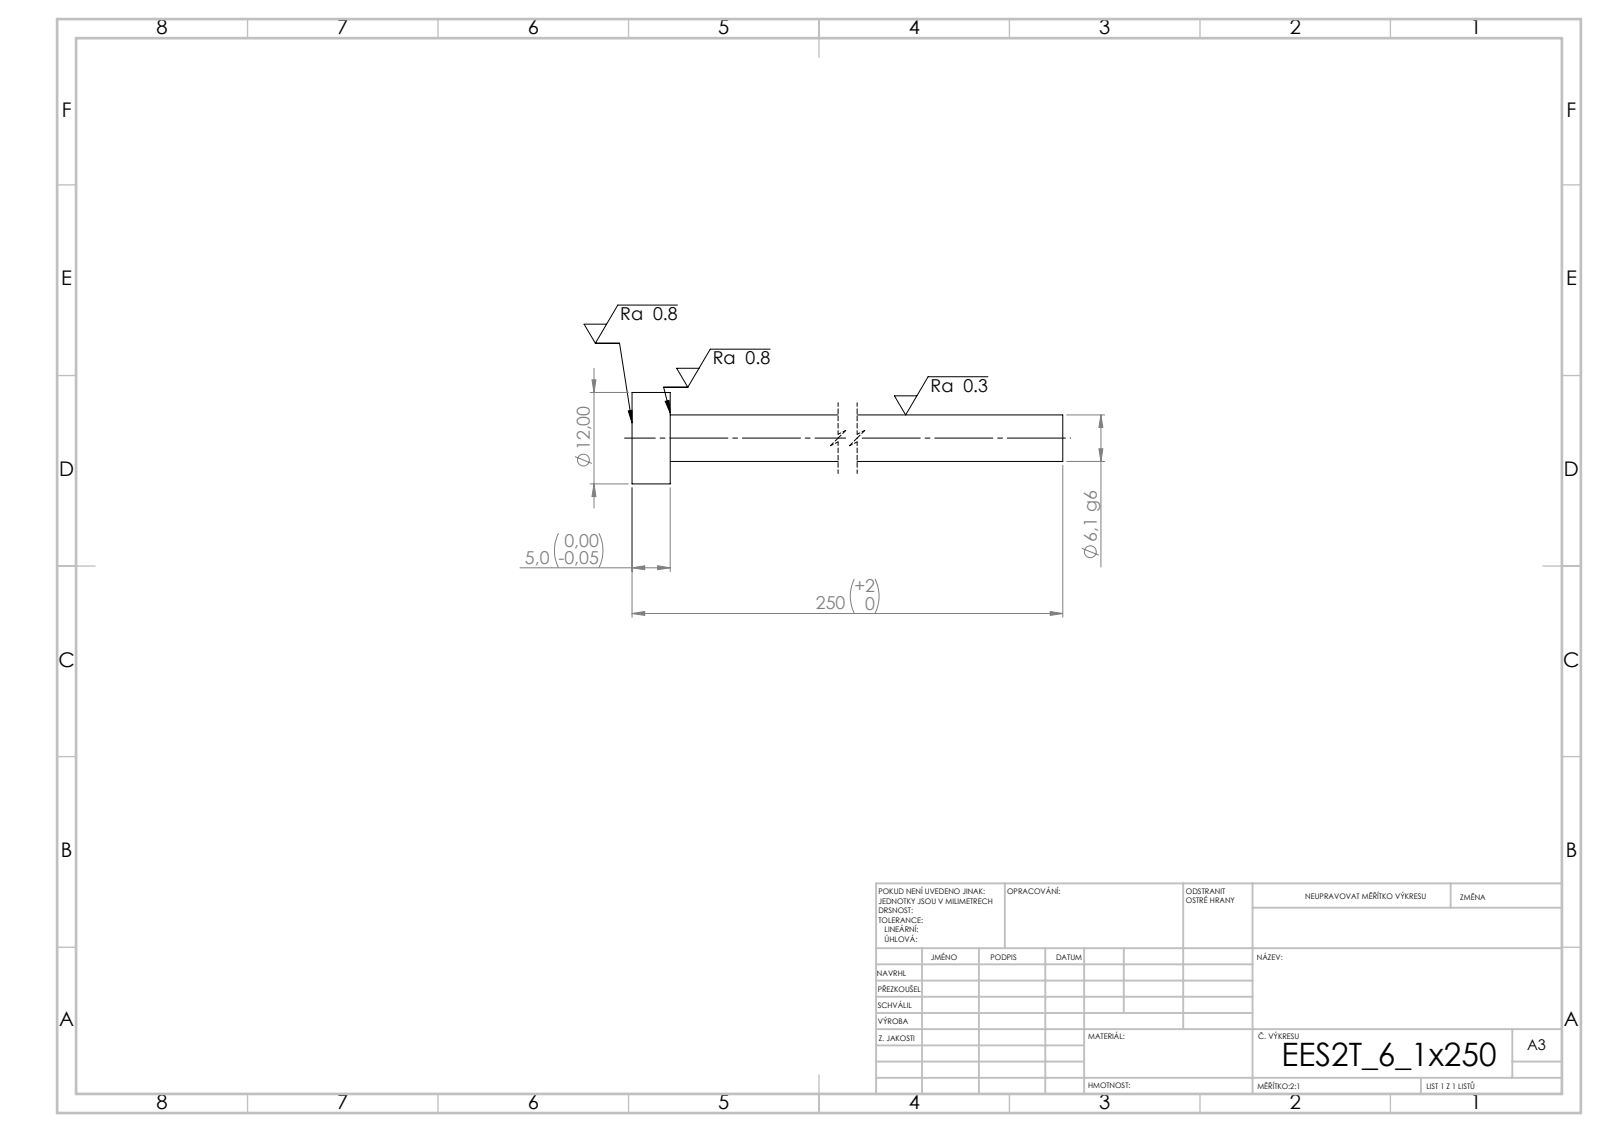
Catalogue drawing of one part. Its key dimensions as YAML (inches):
step_written_by: "SolidWorks 2019 (CONFIG_CONTROL_DESIGN)"
units: inches
bodies: {solids: 1, faces: 7, planar: 3, cylindrical: 4, other: 0}
overall_size: [9.843, 0.472, 0.472]
volume: 0.471
surface_area: 7.921
round_bosses_or_shafts:
  - {diameter: 0.472, count: 1}
  - {diameter: 0.24, count: 1}
face_to_face_distances: [0.197, 9.843, 9.646]
